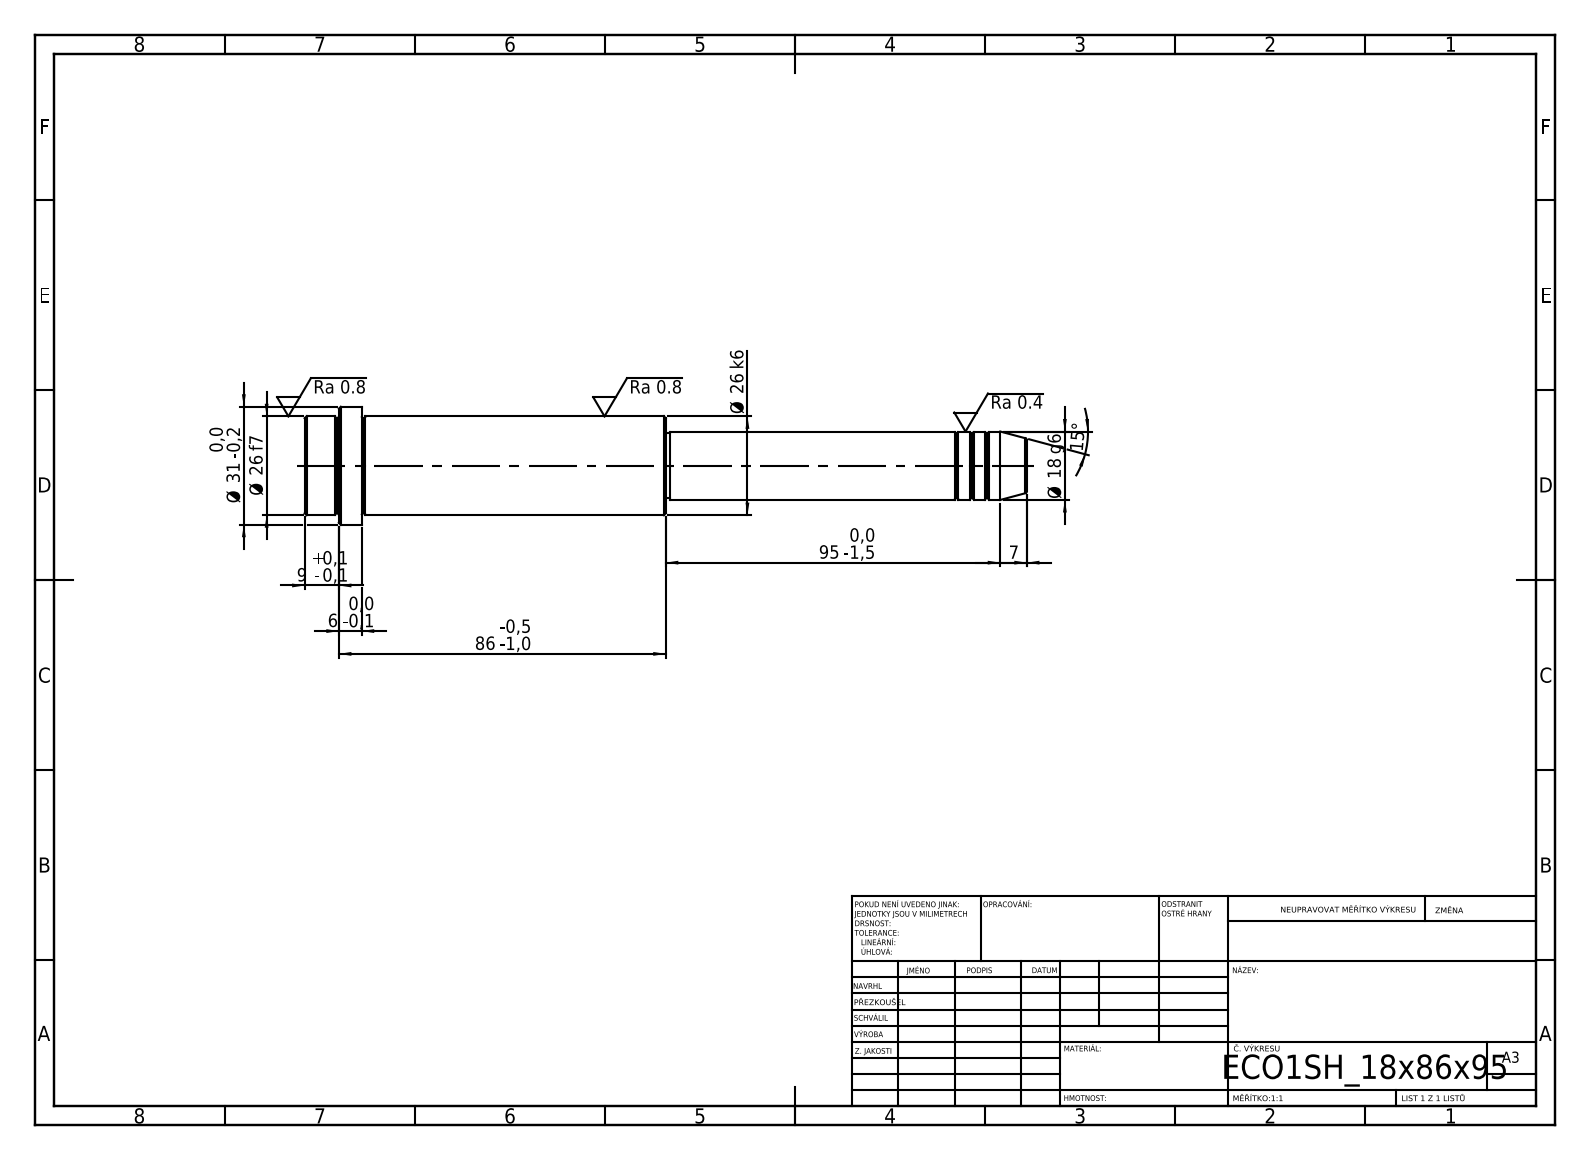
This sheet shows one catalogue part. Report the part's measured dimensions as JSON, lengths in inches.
{"step_written_by": "SolidWorks 2019 (CONFIG_CONTROL_DESIGN)", "units": "inches", "bodies": {"solids": 1, "faces": 52, "planar": 6, "cylindrical": 16, "other": 30}, "overall_size": [7.48, 1.22, 1.22], "volume_in3": 4.602, "surface_area_in2": 22.87, "round_bosses_or_shafts": [[1.22, 1], [1.024, 1], [0.709, 1], [0.669, 1]], "face_to_face_distances": [3.74, 3.15, 0.591, 3.386, 0.236, 0.354, 6.89, 7.126, 7.48, 3.701]}
